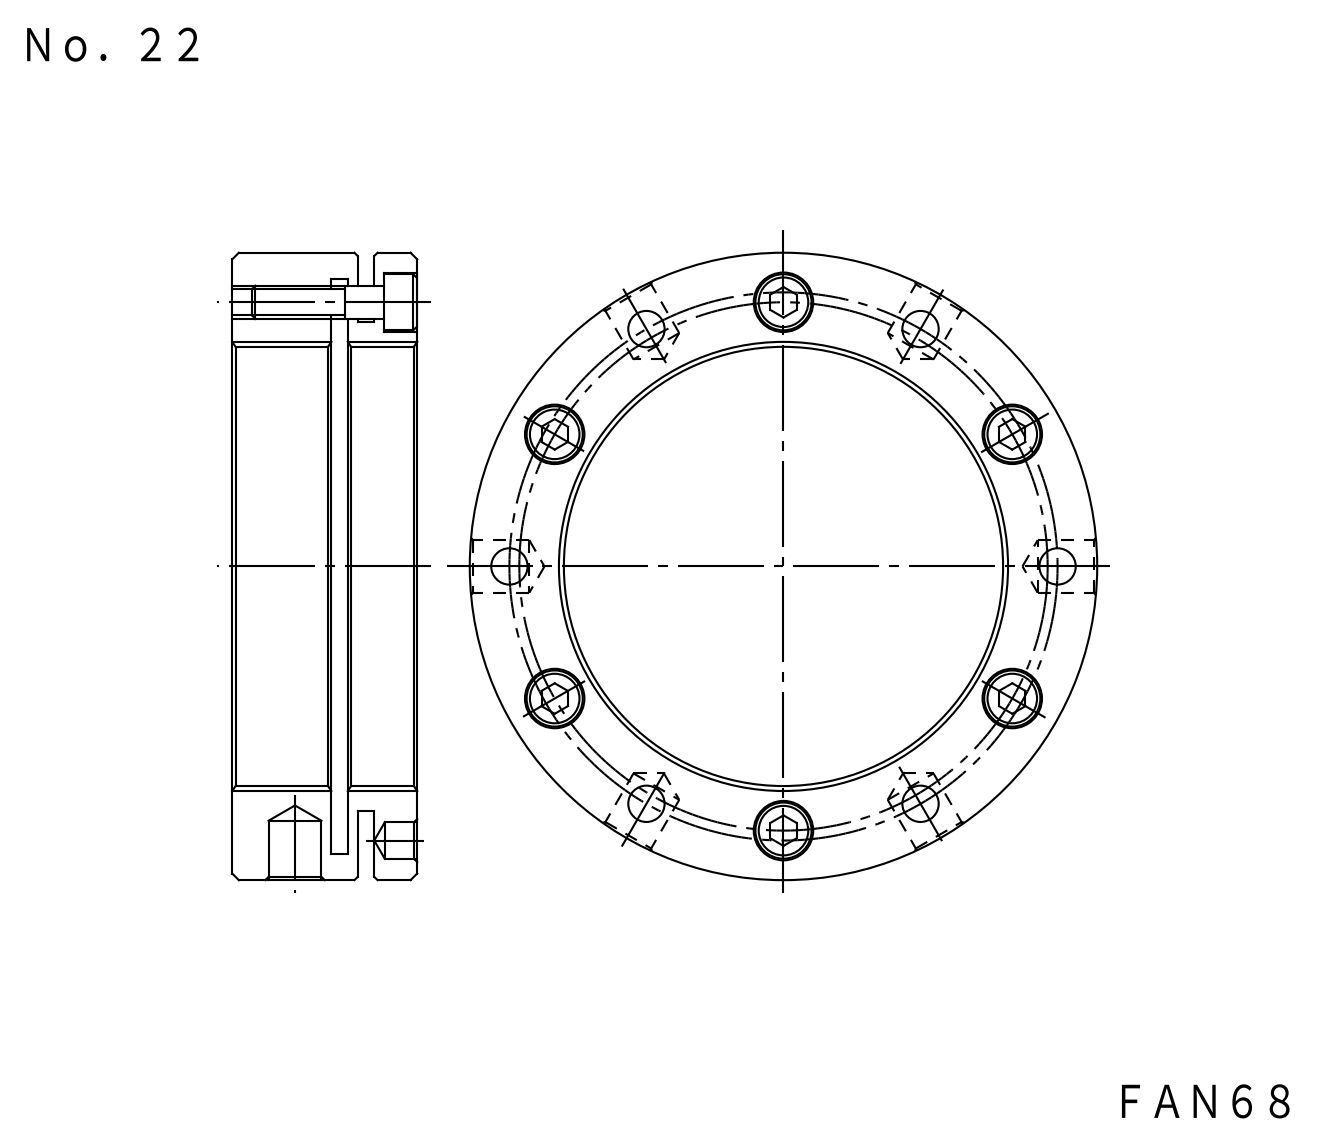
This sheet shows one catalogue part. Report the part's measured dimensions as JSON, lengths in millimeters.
{"part_name": "FKD FAN68; M5X20_default", "step_written_by": "SolidWorks 2012 (CONFIG_CONTROL_DESIGN)", "units": "millimeters", "bodies": {"solids": 7, "faces": 204, "planar": 72, "cylindrical": 108, "other": 24}, "overall_size": [95, 95, 28], "volume_mm3": 81124, "surface_area_mm2": 38233, "round_holes": [[4.13, 6], [5.3, 6], [5.5, 6], [9, 6], [8, 3], [68, 1], [88, 1]], "round_bosses_or_shafts": [[8.5, 6], [5, 6], [95, 1], [76, 1]], "face_to_face_distances": [2.5, 4, 14, 28, 18, 10, 20.5, 7.5, 6.5, 16.5], "hole_center_spacings": [21.36, 41, 41.5, 58.34, 79.69, 71.02, 71.88, 83]}
